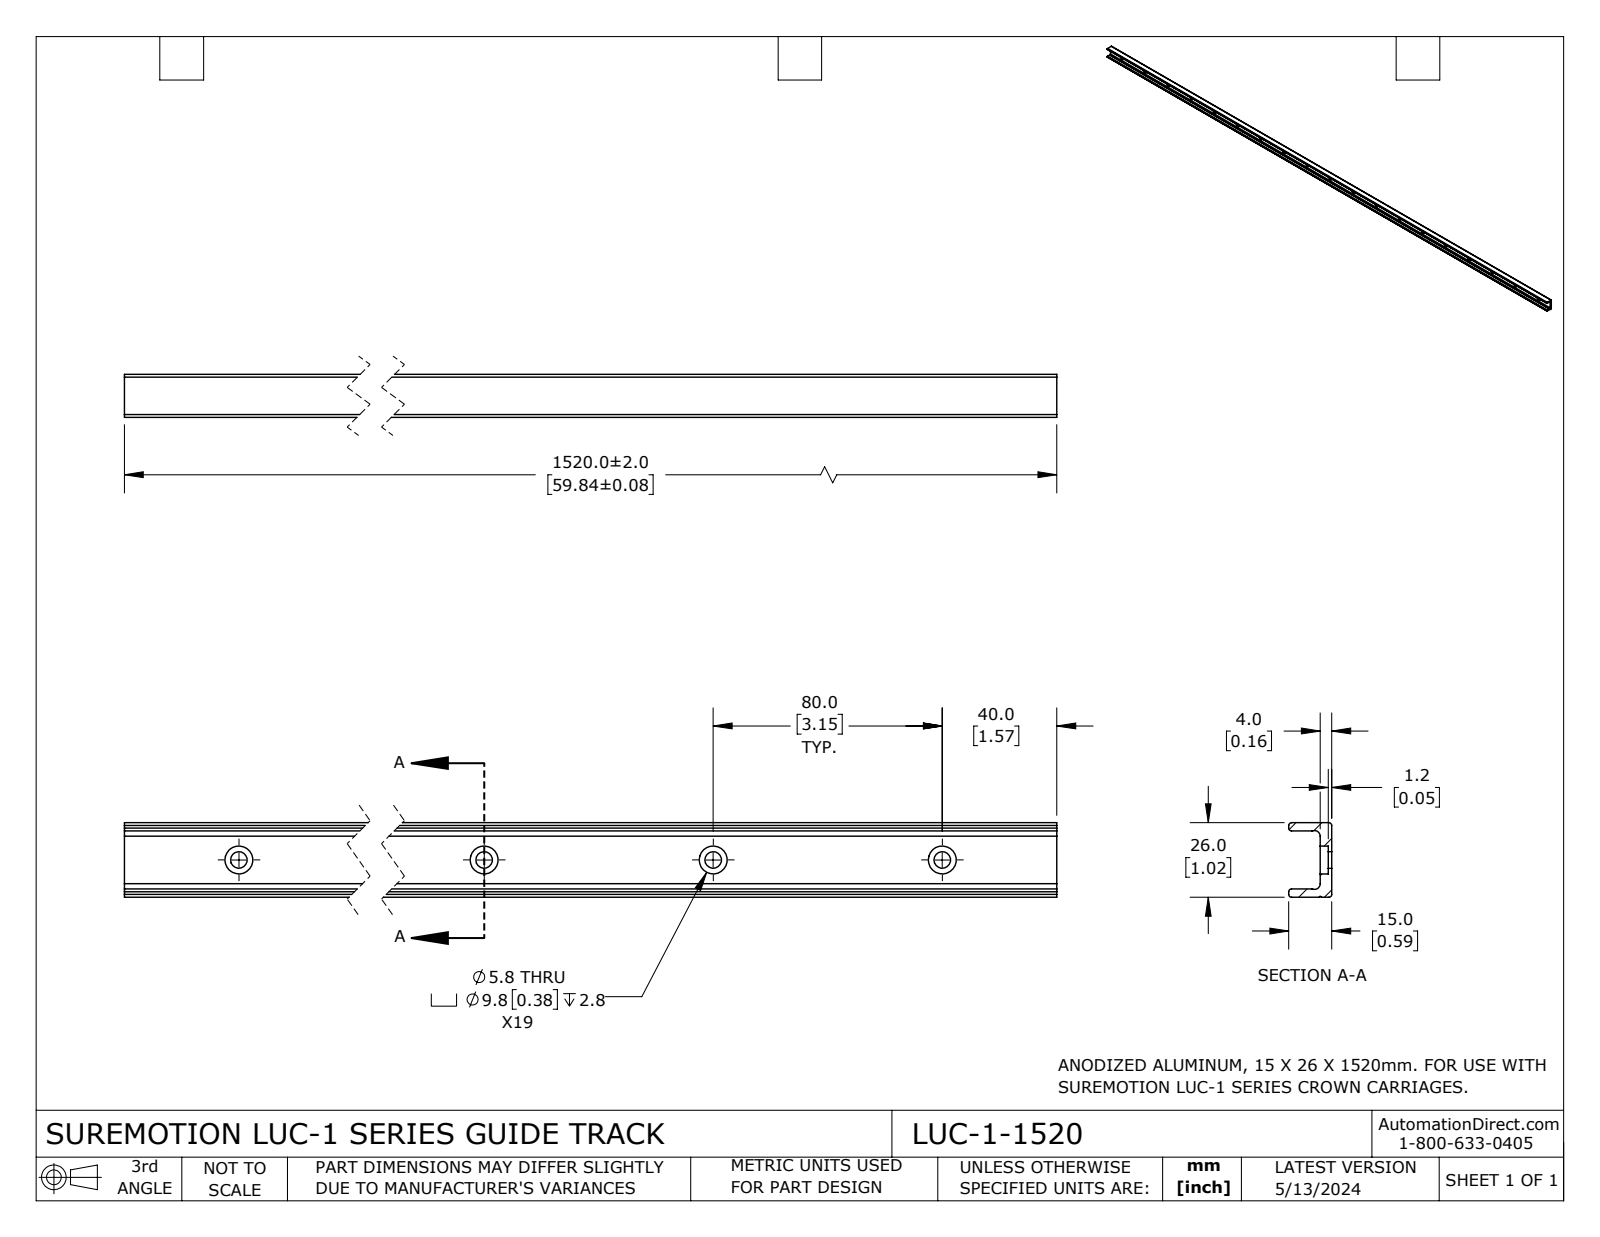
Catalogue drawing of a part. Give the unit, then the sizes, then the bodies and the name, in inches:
Units: inches
Overall size (bounding box): 59.843 × 1.024 × 0.591
Round holes (diameter × count): ⌀0.228 ×19, ⌀0.384 ×19
Partial cylindrical surfaces — rounded edges, fillets, slot ends (radius × count): R0.039 ×8, R0.078 ×2, R0.013 ×1
Main face-to-face distances: 0.158, 0.114, 0.91, 1.024, 0.796, 0.591, 0.433, 0.048, 0.11, 0.544
Hole centre spacings: 3.15, 6.299, 9.449, 12.598, 15.748, 18.898, 22.047, 25.197
Volume: 15.26 in³ · Surface area: 238.9 in²
Bodies: 1 solid, 117 faces (30 planar, 87 cylindrical, 0 other)
Part name (STEP PRODUCT): LUC-1-1520
STEP written by: SolidWorks 2023 (CONFIG_CONTROL_DESIGN)
